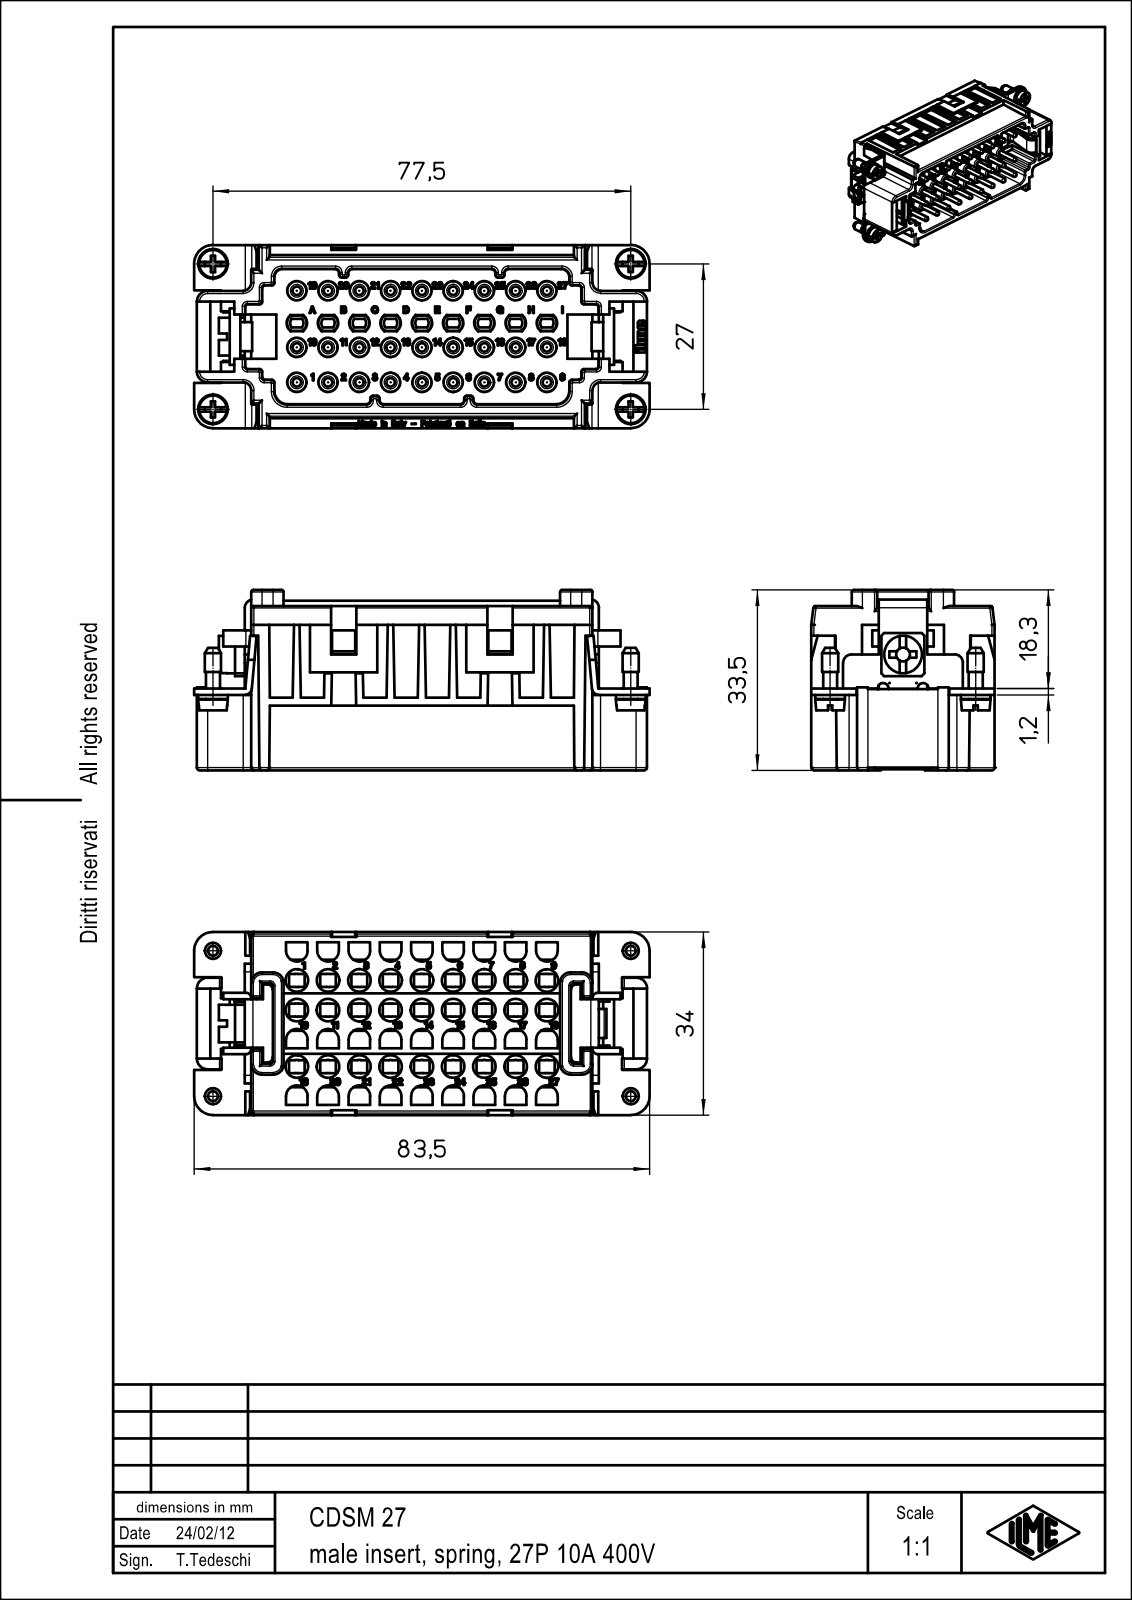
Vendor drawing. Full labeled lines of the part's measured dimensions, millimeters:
Part name (STEP PRODUCT): CDSM_27
STEP written by: Creo Elements/Direct Modeling 17.0D 15-Jul-2011 (C) Parametric Technology GmbH (AUTOMOTIVE_DESIGN)
Units: millimetres
Bodies: 1 solid, 6617 faces (5843 planar, 422 cylindrical, 352 other)
Overall size (bounding box): 84.5 × 34 × 33.5
Volume: 46 701 mm³ · Surface area: 24 112 mm²
Round holes (diameter × count): ⌀4.2 ×27, ⌀2.58 ×1, ⌀3 ×1
Round bosses / shafts (diameter × count): ⌀1.6 ×27, ⌀5.5 ×4, ⌀3 ×4, ⌀2.6 ×4, ⌀7 ×1
Partial cylindrical surfaces — rounded edges, fillets, slot ends (radius × count): R0.5 ×60, R2 ×41, R0.4 ×19, R1 ×14, R1.5 ×10, R1.25 ×9, R1.9 ×9, R0.8 ×8
Main face-to-face distances: 0.9, 2, 13, 1.2, 33.1, 18.5, 1, 8.5, 7.6, 15
Hole centre spacings: 5.8, 11.6, 17.4, 7.99, 12, 17.02, 23.2, 12.84
